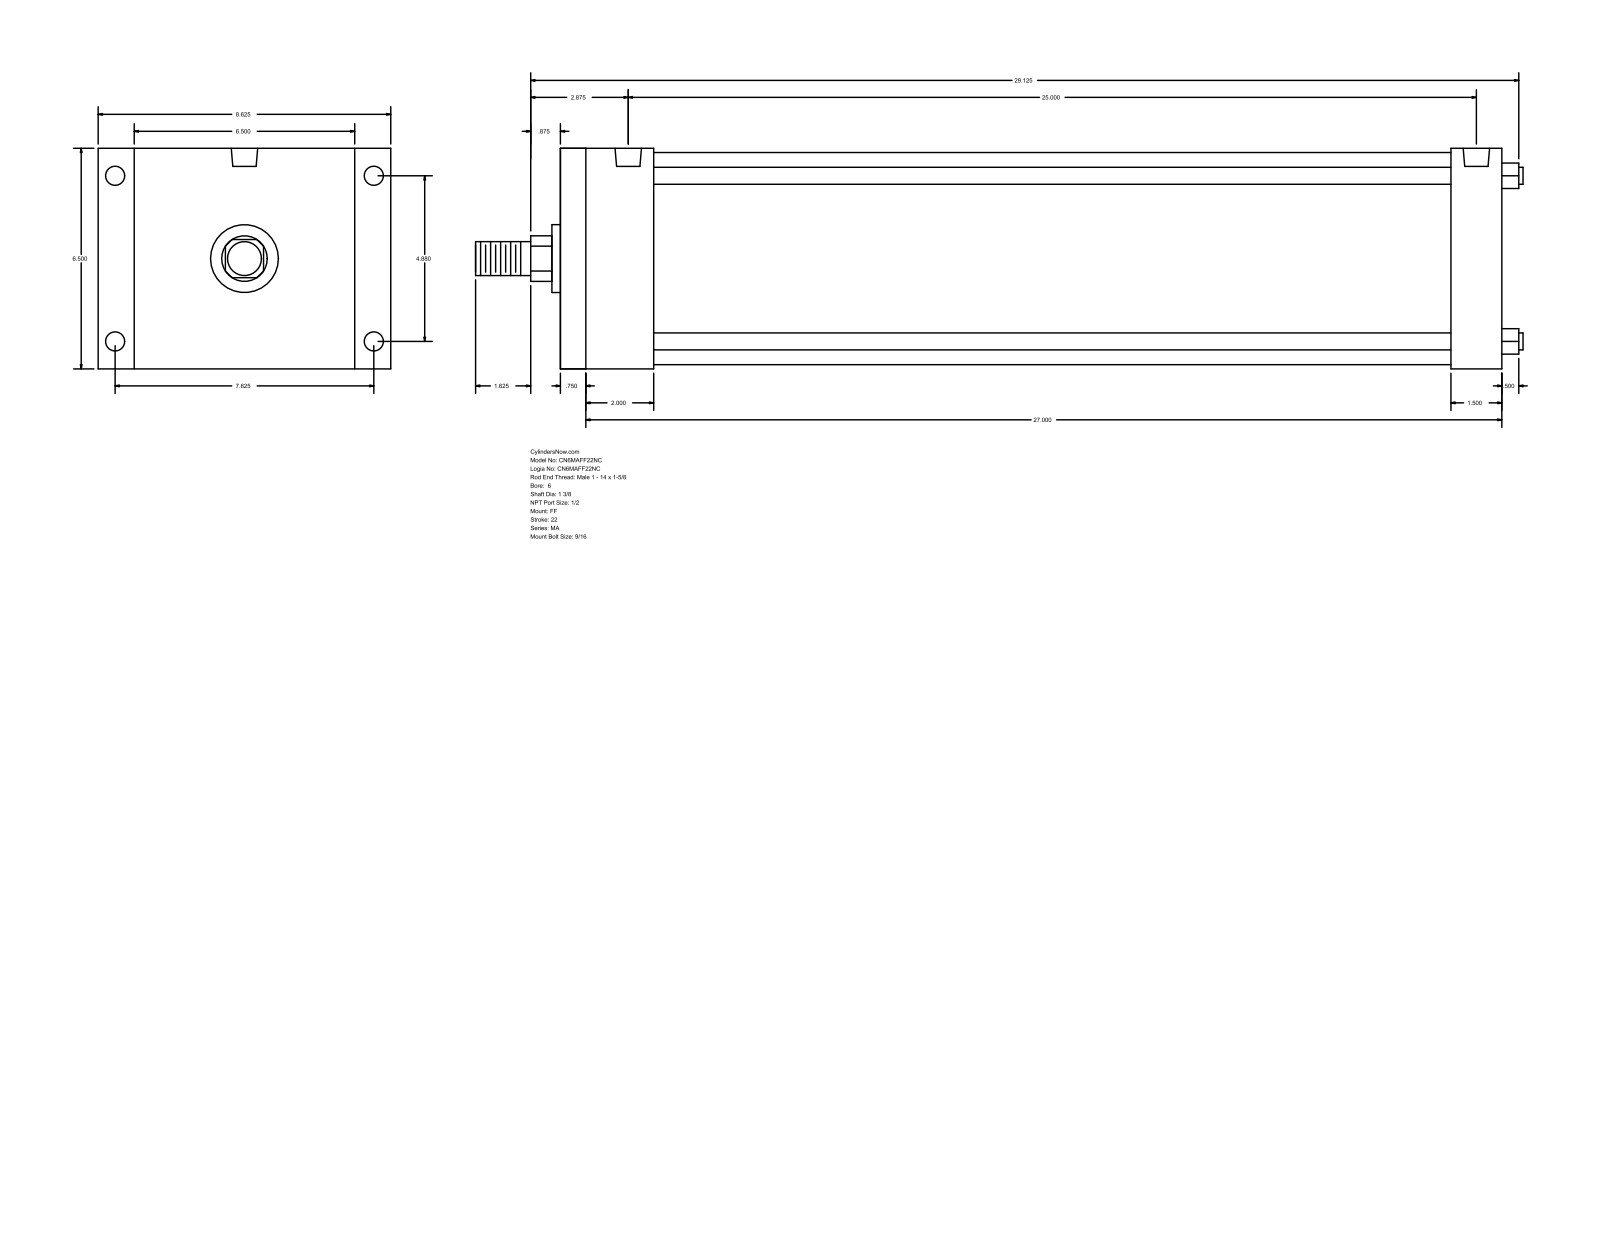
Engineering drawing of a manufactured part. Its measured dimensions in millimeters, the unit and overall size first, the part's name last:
Units: millimetres
Overall size (bounding box): 784.23 × 219.07 × 165.1
Round holes (diameter × count): ⌀14.29 ×4, ⌀17.46 ×4, ⌀19.77 ×2
Round bosses / shafts (diameter × count): ⌀12.7 ×4, ⌀158.75 ×1, ⌀50.8 ×1, ⌀34.92 ×1, ⌀25.4 ×1
Partial cylindrical surfaces — rounded edges, fillets, slot ends (radius × count): R17.06 ×1
Main face-to-face distances: 165.1, 704.85, 15.87, 688.98, 38.1, 66.67, 50.8, 638.18, 666.75, 650.88
Hole centre spacings: 123.96, 193.68, 229.95, 638.17, 3.18, 634.99
Bodies: 0 solids, 92 faces (64 planar, 28 cylindrical, 0 other)
Part name (STEP PRODUCT): MA_FF__0600_1.375
STEP written by: GSSL Pune (CONFIG_CONTROL_DESIGN)
